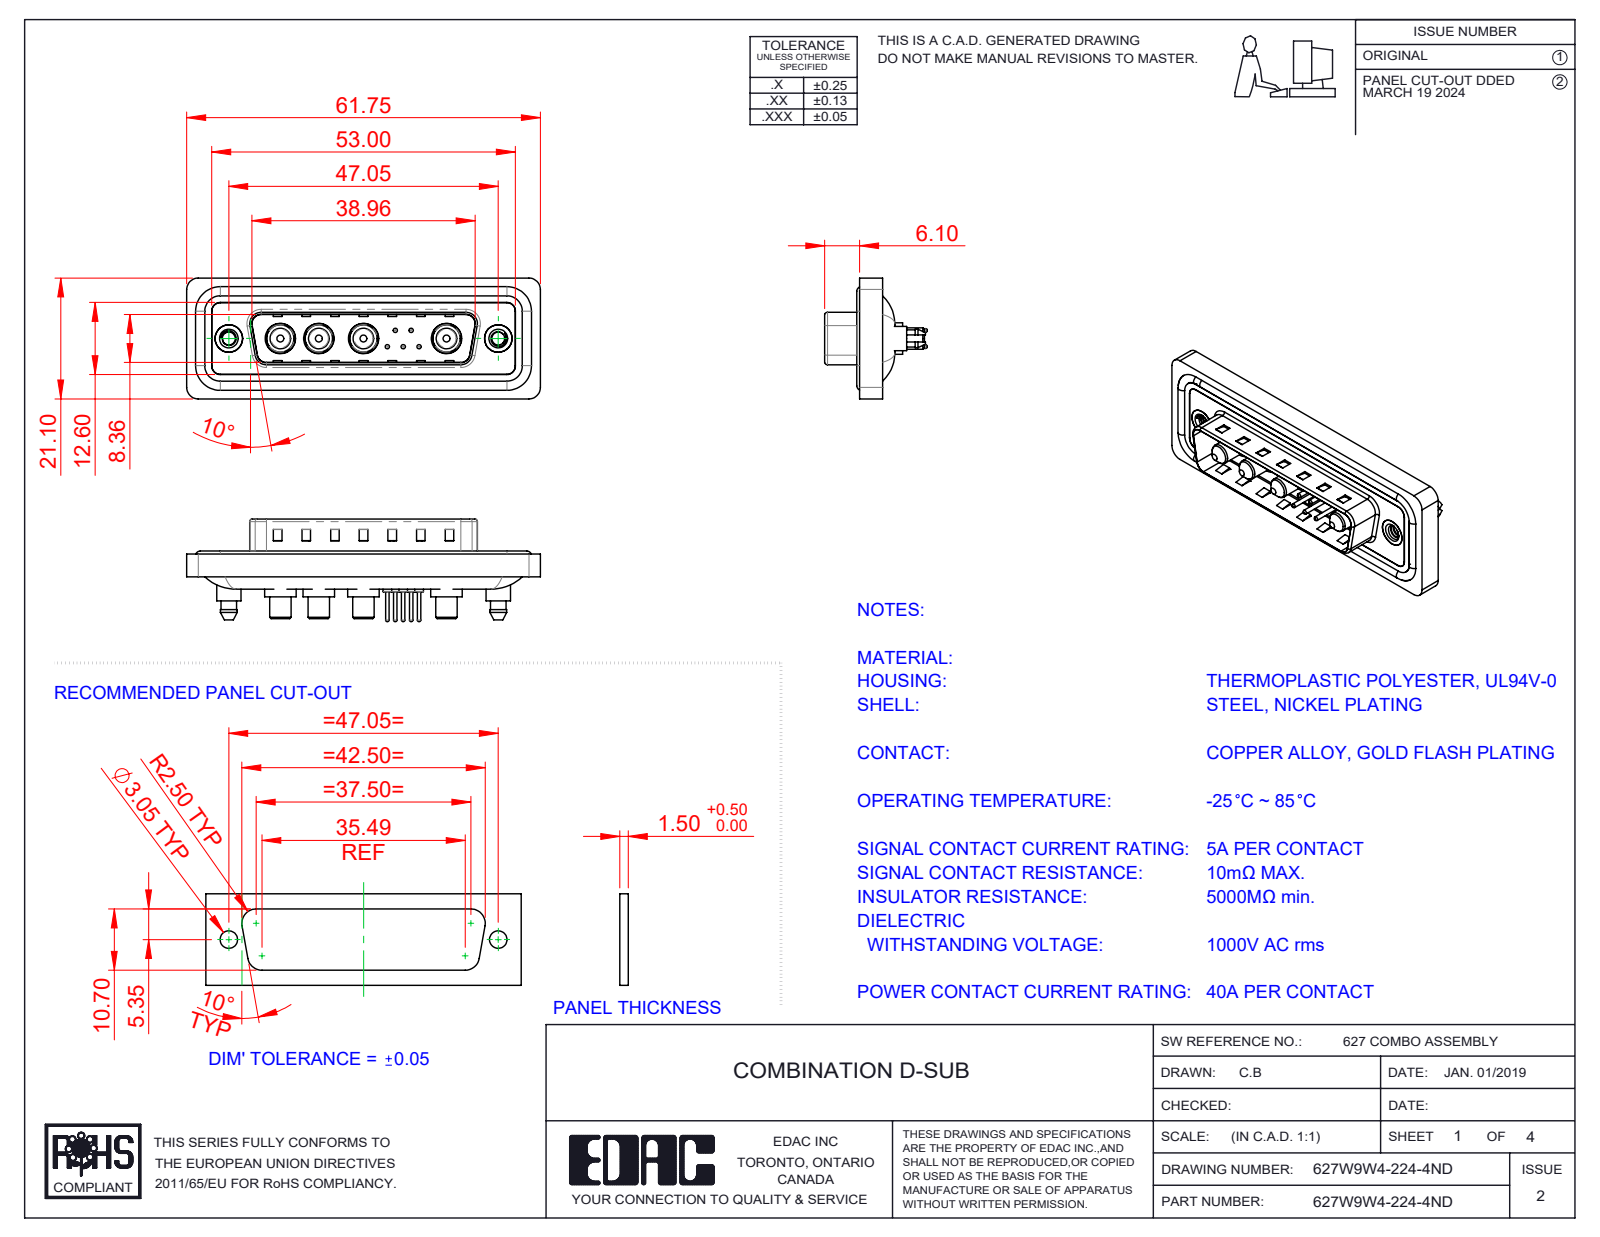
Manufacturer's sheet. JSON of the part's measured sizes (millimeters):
{"part_name": "627Combo Waterproof Housing_25 Contacts; 627Combo Contact Row 2_24; 627Combo Shell Rear_25 Contacts; 627Combo Threaded Boardlock_D (+6 more)", "step_written_by": "SolidWorks 2023 (CONFIG_CONTROL_DESIGN)", "units": "millimeters", "bodies": {"solids": 20, "faces": 882, "planar": 300, "cylindrical": 374, "other": 208}, "overall_size": [61.75, 21.1, 17.9], "volume_mm3": 7612, "surface_area_mm2": 12215, "round_holes": [[0.75, 5], [1.6, 5], [2, 5], [4.85, 4], [5.3, 4], [2.26, 2], [4, 2], [4.8, 2], [5, 2]], "round_bosses_or_shafts": [[1.5, 5], [0.6, 5], [5.5, 4], [5.2, 4], [4.75, 4], [3.75, 4], [3.6, 4], [1.6, 4]], "partial_cylinders_radius": [[1.5, 24], [2, 18], [1.6, 10], [0.5, 8], [0.25, 4], [0.6, 4], [0.65, 4], [0.9, 4]], "face_to_face_distances": [0.4, 1.5, 1.1, 0.5, 3.1, 1.6, 2.9, 0.82, 9.58, 5.65], "hole_center_spacings": [3.16, 2.77, 5.04, 14.51, 2.78, 4.4, 4.41, 5]}
